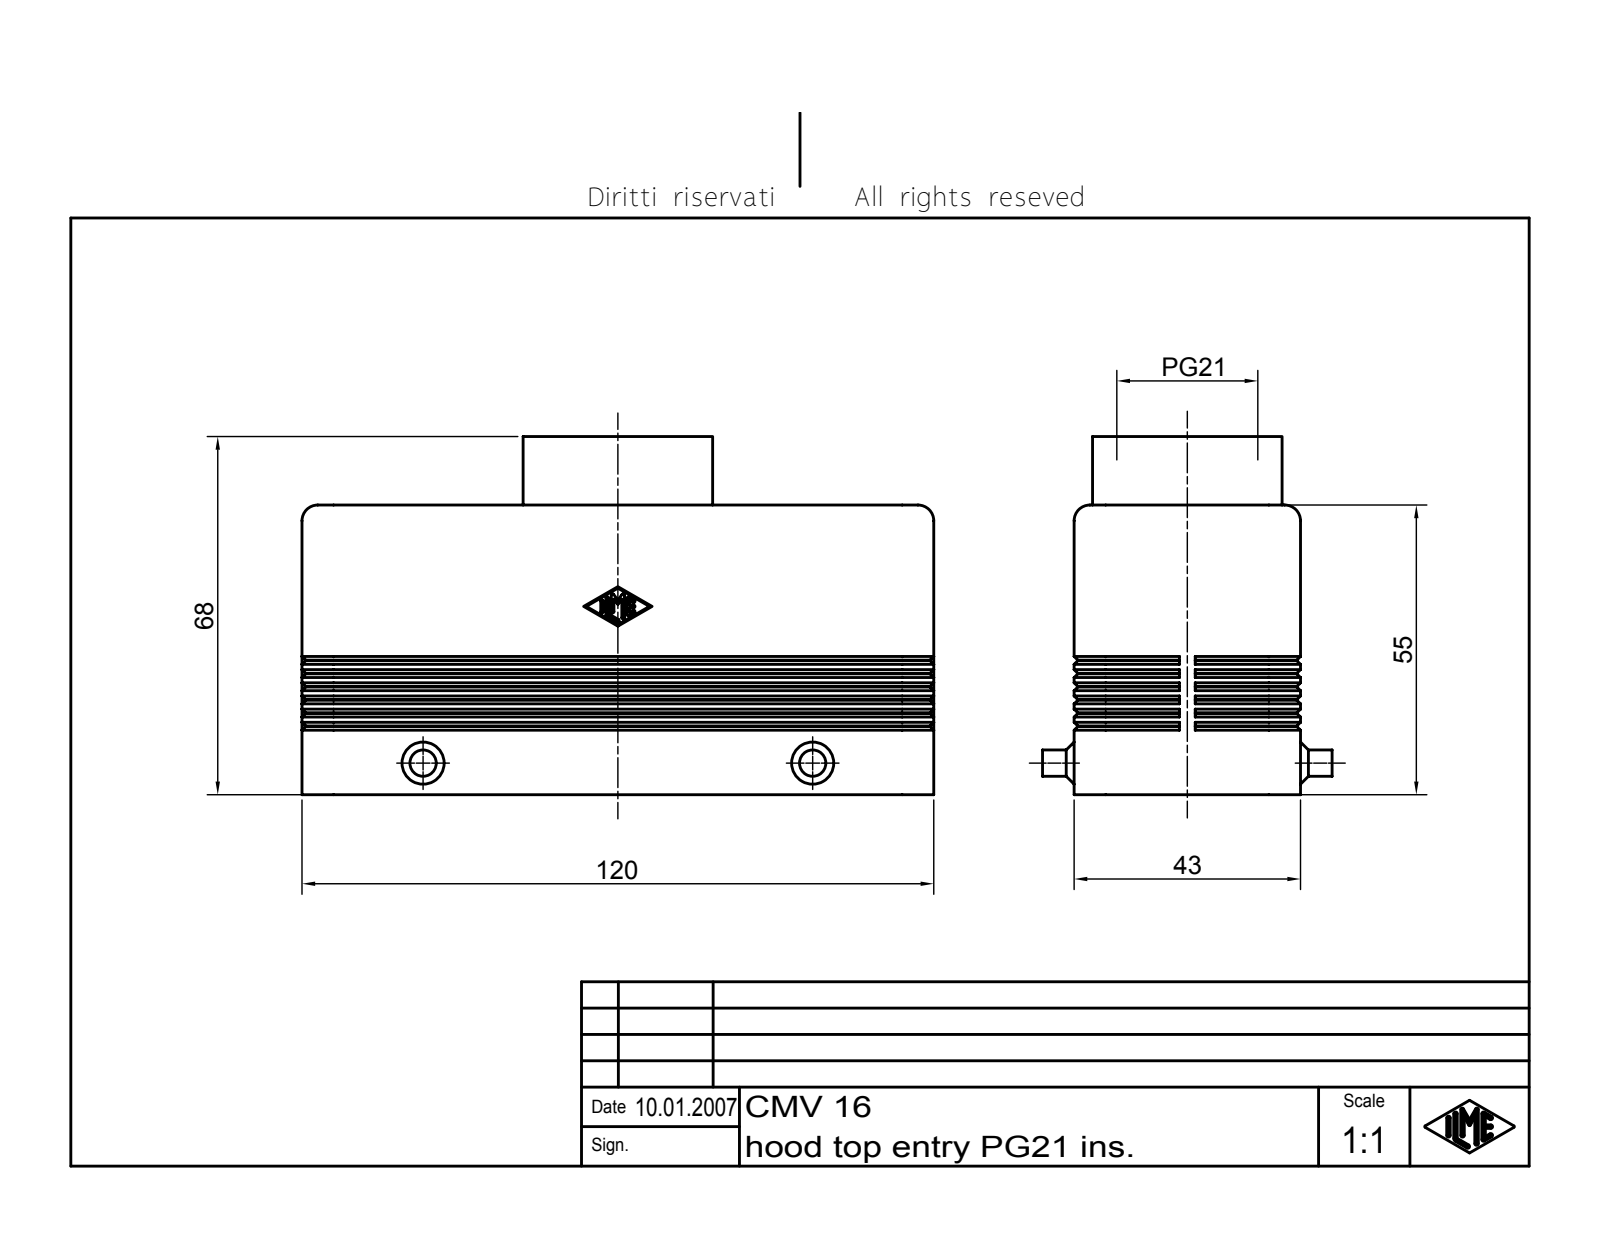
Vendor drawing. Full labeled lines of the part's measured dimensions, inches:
Part name (STEP PRODUCT): CHV Tüllengehäuse 2 Bügel für einen Einsatz
STEP written by: Autodesk Inventor 7 (AUTOMOTIVE_DESIGN)
Units: inches
Bodies: 1 solid, 488 faces (181 planar, 113 cylindrical, 194 other)
Overall size (bounding box): 4.724 × 2.677 × 2.165
Volume: 4.84 in³ · Surface area: 72.77 in²
Round holes (diameter × count): ⌀0.851 ×1, ⌀1.054 ×1
Round bosses / shafts (diameter × count): ⌀0.197 ×2, ⌀1.417 ×1
Partial cylindrical surfaces — rounded edges, fillets, slot ends (radius × count): R0.01 ×14, R0.118 ×8, R0.079 ×4, R0.236 ×4, R0.209 ×2, R0.059 ×1
Main face-to-face distances: 0.118, 1.575, 1.457, 1.693, 0.453, 0.335, 0.07, 4.606, 0.209, 4.724
